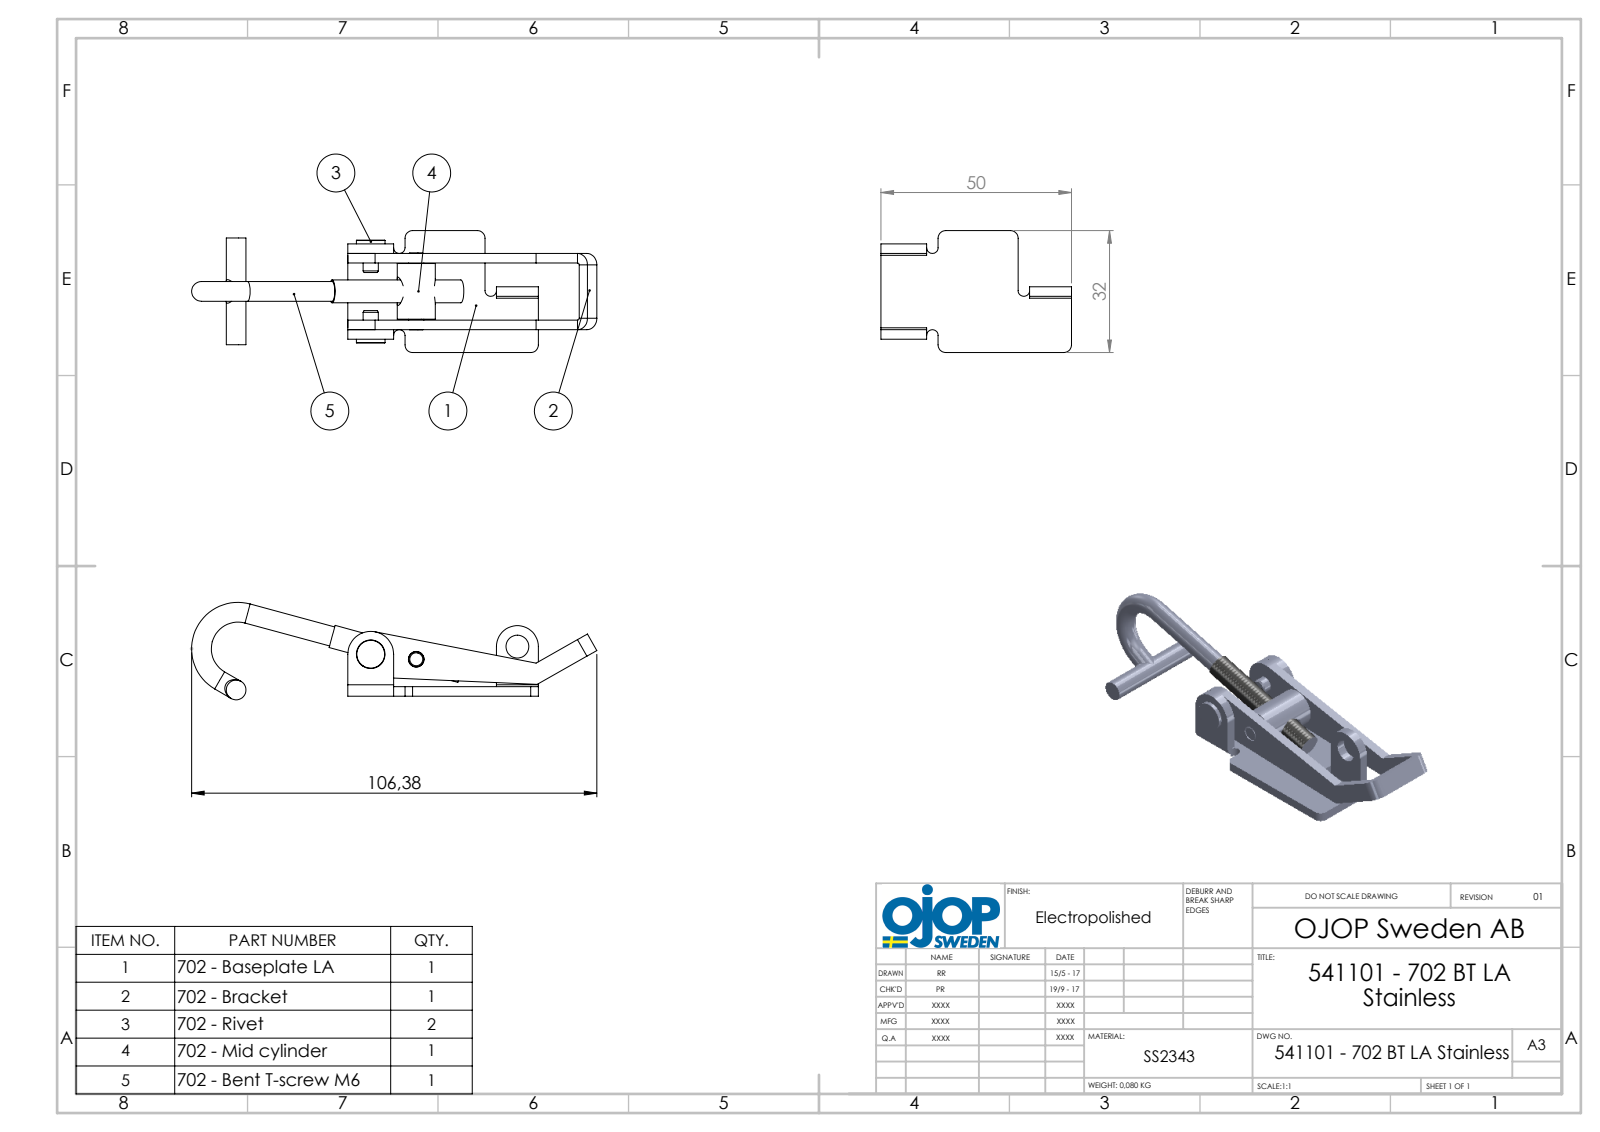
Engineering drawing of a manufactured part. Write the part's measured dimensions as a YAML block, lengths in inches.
part_name: "702 - Bygel; 541101 - 702 BT LA Stainless; 702 - Rulle; 702 - Böjd T-skruv M6 (+2 more)"
step_written_by: "SolidWorks 2015 (AUTOMOTIVE_DESIGN)"
units: inches
bodies: {solids: 6, faces: 152, planar: 66, cylindrical: 66, other: 20}
overall_size: [4.213, 1.26, 1.006]
volume: 0.661
surface_area: 16
round_holes:
  - {diameter: 0.161, count: 2}
  - {diameter: 0.236, count: 2}
  - {diameter: 0.197, count: 1}
round_bosses_or_shafts:
  - {diameter: 0.204, count: 3}
  - {diameter: 0.157, count: 2}
  - {diameter: 0.394, count: 1}
  - {diameter: 0.295, count: 1}
  - {diameter: 0.236, count: 1}
partial_cylinders:
  - {radius: 0.02, count: 5}
  - {radius: 0.118, count: 5}
  - {radius: 0.079, count: 4}
  - {radius: 0.059, count: 2}
  - {radius: 0.059, count: 1}
  - {radius: 0.217, count: 1}
  - {radius: 0.236, count: 1}
face_to_face_distances: [0.098, 0.689, 0.787, 0.344, 0.443, 0.591, 0.197, 0.246, 0.886, 0.236]
hole_center_spacings: [0.473, 1.055, 1.518]
